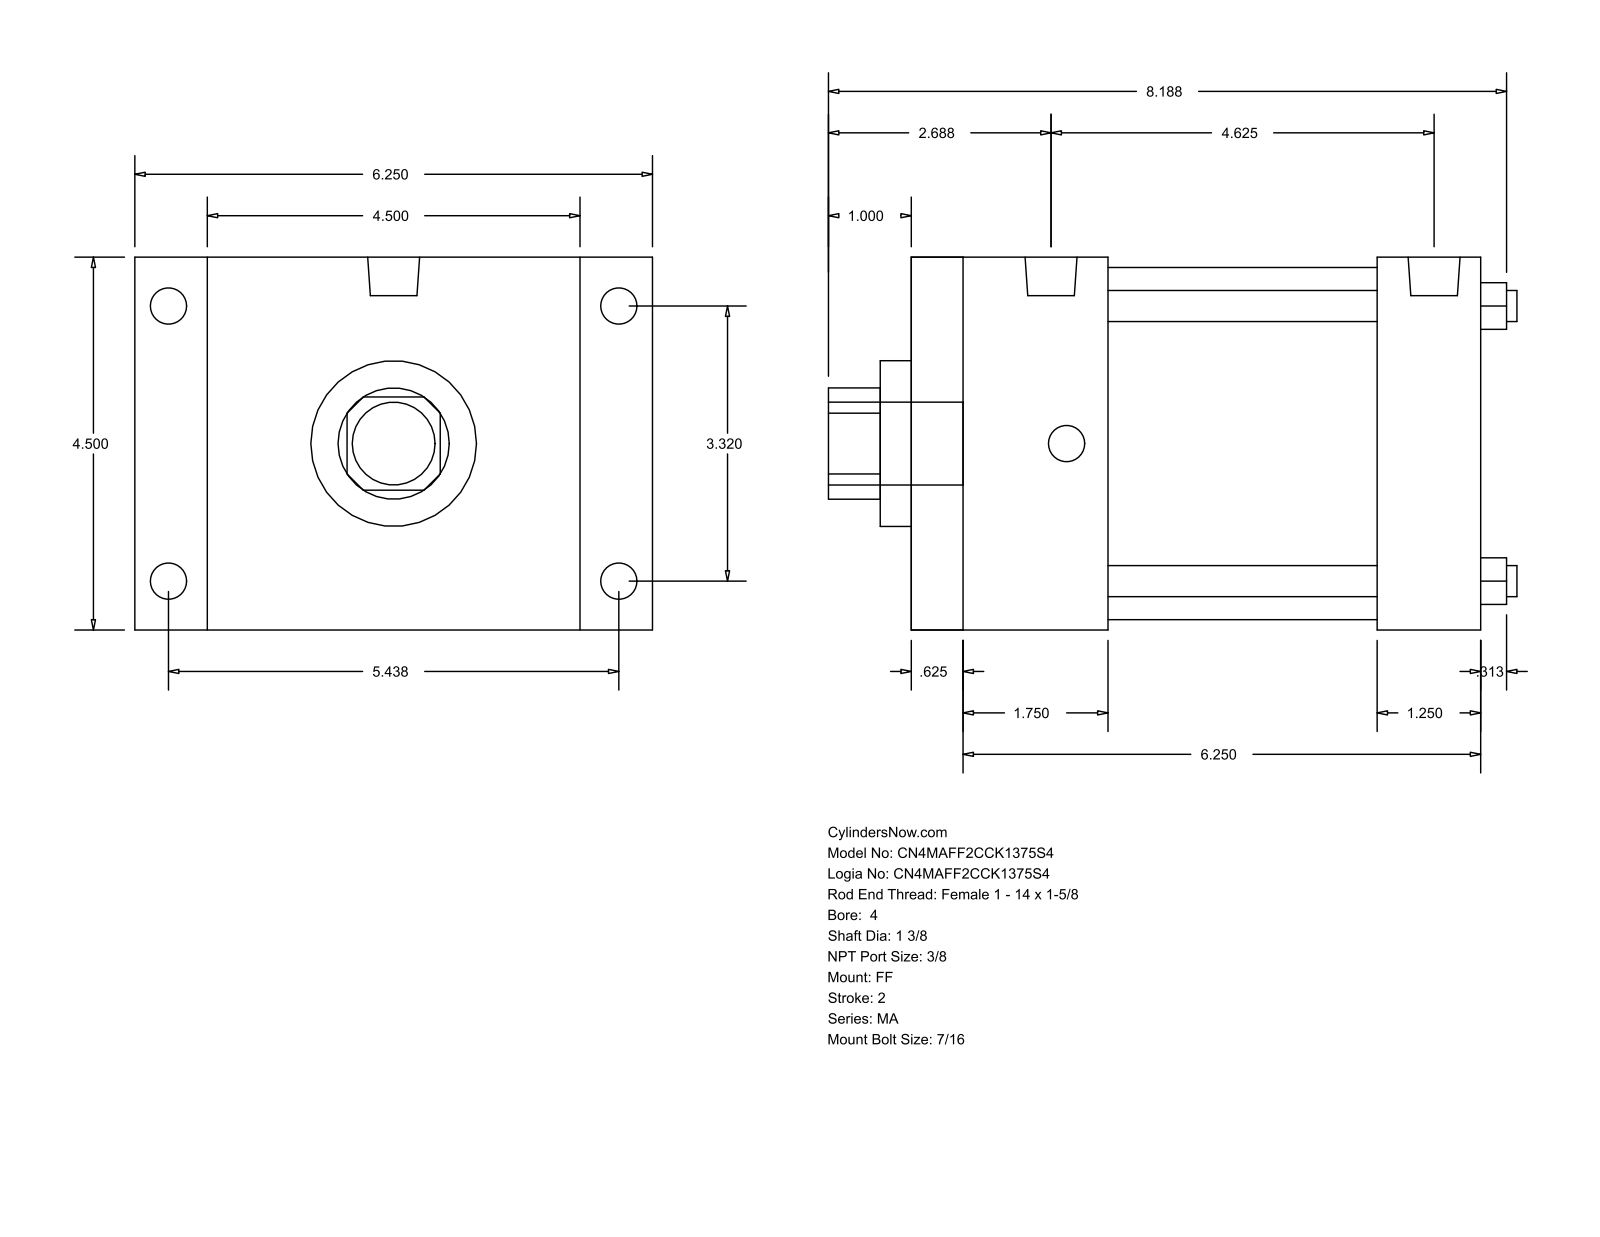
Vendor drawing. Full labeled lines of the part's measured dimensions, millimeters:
Part name (STEP PRODUCT): MA_FF__0400_1.375
STEP written by: GSSL Pune (CONFIG_CONTROL_DESIGN)
Units: millimetres
Bodies: 0 solids, 92 faces (64 planar, 28 cylindrical, 0 other)
Overall size (bounding box): 211.14 × 158.75 × 114.3
Round holes (diameter × count): ⌀9.53 ×4, ⌀34.92 ×1, ⌀50.8 ×1, ⌀107.95 ×1
Round bosses / shafts (diameter × count): ⌀11.11 ×8, ⌀15.93 ×2, ⌀25.4 ×1
Partial cylindrical surfaces — rounded edges, fillets, slot ends (radius × count): R17.06 ×1
Main face-to-face distances: 114.3, 174.63, 158.76, 15.87, 22.23, 136.53, 142.88, 127.01, 31.75, 60.32
Hole centre spacings: 59.62, 84.32, 119.25
